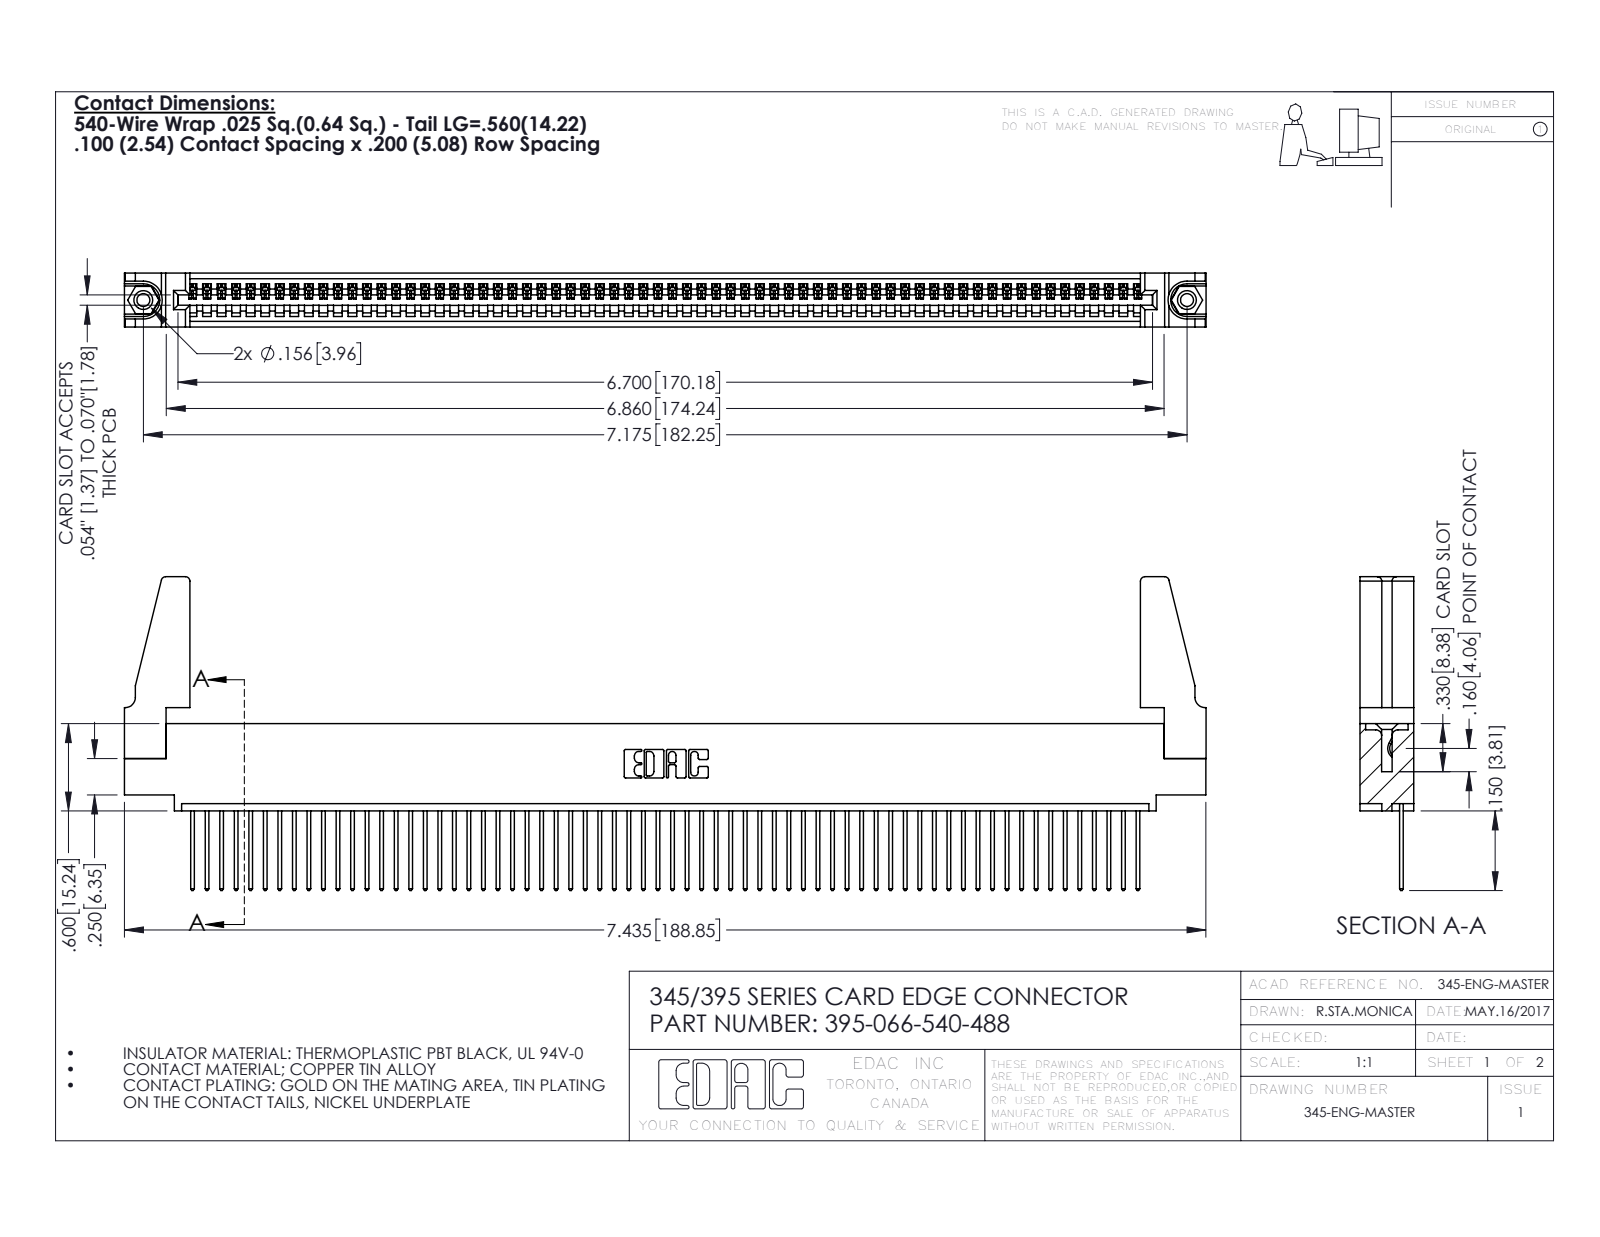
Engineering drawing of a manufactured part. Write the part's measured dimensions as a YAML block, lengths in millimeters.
part_name: "345-220-078_345-220-088; 345-250-001_345-250-001-102; 345-292-001_345-293-140; 395-066-540-488 (+1 more)"
step_written_by: "SolidWorks 2016 (CONFIG_CONTROL_DESIGN)"
units: millimeters
bodies: {solids: 71, faces: 4082, planar: 2796, cylindrical: 1270, other: 16}
overall_size: [188.9, 54.8, 9.4]
volume: 21400
surface_area: 28300
round_holes:
  - {diameter: 2.3, count: 2}
  - {diameter: 3.2, count: 2}
  - {diameter: 4, count: 2}
  - {diameter: 1.6, count: 1}
round_bosses_or_shafts:
  - {diameter: 3.9, count: 2}
partial_cylinders:
  - {radius: 0.2, count: 132}
  - {radius: 0.3, count: 132}
  - {radius: 0.3, count: 22}
  - {radius: 0.8, count: 8}
  - {radius: 0.2, count: 6}
  - {radius: 0.8, count: 6}
  - {radius: 0.7, count: 3}
  - {radius: 0.8, count: 2}
face_to_face_distances: [1.8, 7.6, 9.4, 2.5, 6.9, 0.6, 5.1, 5.7, 3.8, 1.8]
hole_center_spacings: [6.9, 176.3, 182.2]
